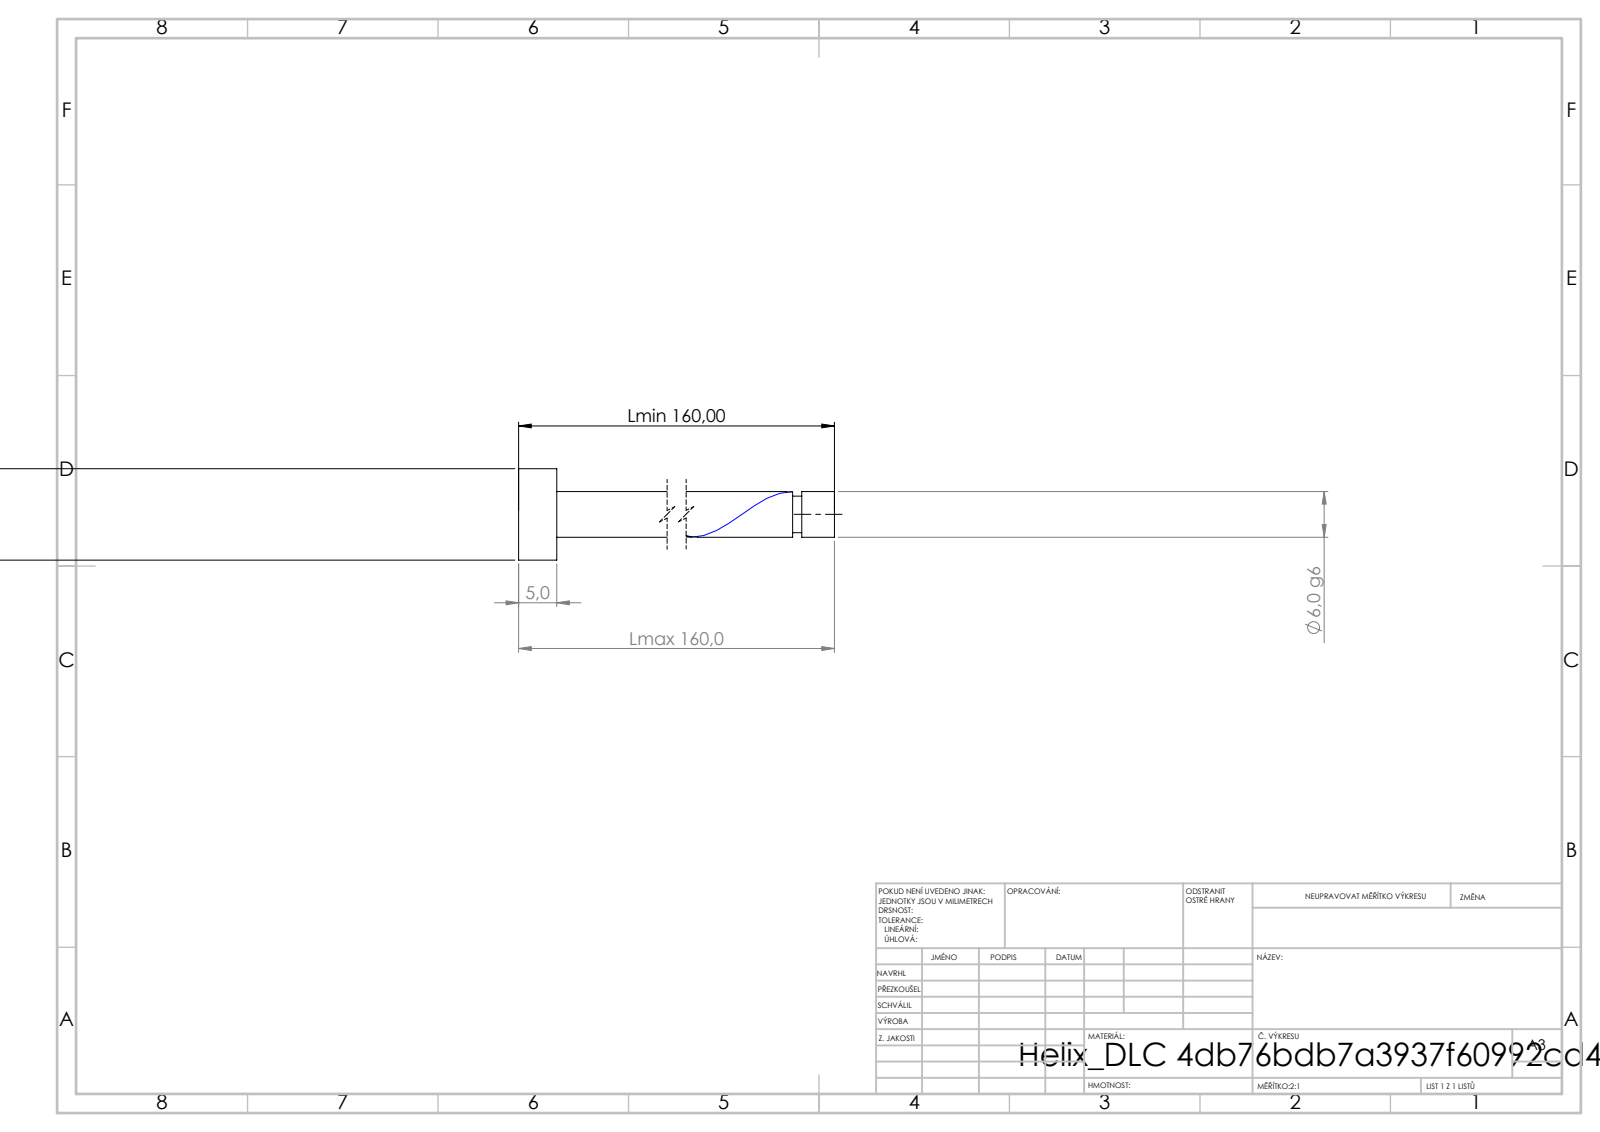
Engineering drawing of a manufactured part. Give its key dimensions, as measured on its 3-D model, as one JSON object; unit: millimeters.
{"step_written_by": "SolidWorks 2019 (CONFIG_CONTROL_DESIGN)", "units": "millimeters", "bodies": {"solids": 1, "faces": 21, "planar": 6, "cylindrical": 14, "other": 1}, "overall_size": [160, 12, 12], "volume_mm3": 4892, "surface_area_mm2": 3412, "round_bosses_or_shafts": [[12, 1], [6, 1], [4.8, 1]], "face_to_face_distances": [5, 160, 155, 155.71, 150.71, 4.29, 154.51, 149.51, 1.2, 5.49]}
